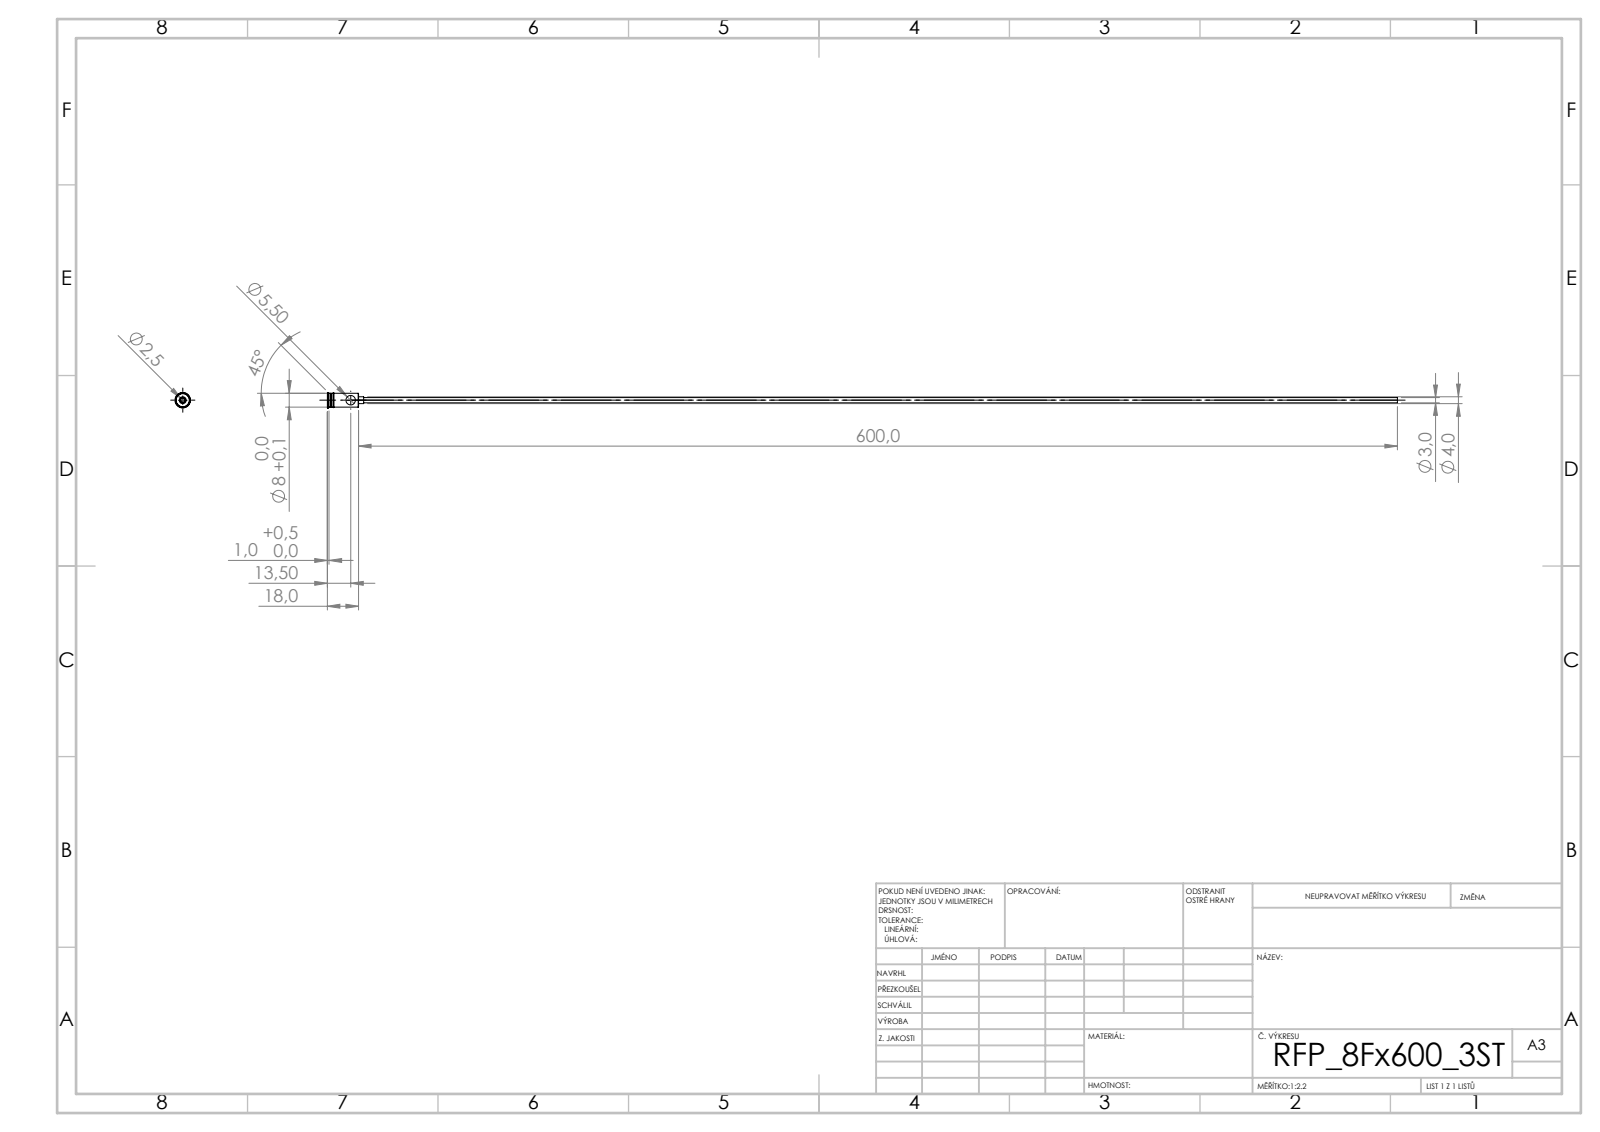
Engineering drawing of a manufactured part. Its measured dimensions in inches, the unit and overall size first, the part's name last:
Units: inches
Overall size (bounding box): 24.331 × 0.354 × 0.354
Round holes (diameter × count): ⌀0.098 ×1, ⌀0.217 ×1
Round bosses / shafts (diameter × count): ⌀0.354 ×1, ⌀0.315 ×1, ⌀0.157 ×1, ⌀0.118 ×1
Main face-to-face distances: 0.709, 0.134, 0.63, 0.079, 0.618, 0.091, 0.118, 0.736, 0.748, 0.827
Volume: 0.123 in³ · Surface area: 17.15 in²
Bodies: 1 solid, 44 faces (20 planar, 16 cylindrical, 8 other)
STEP written by: SolidWorks 2019 (CONFIG_CONTROL_DESIGN)
